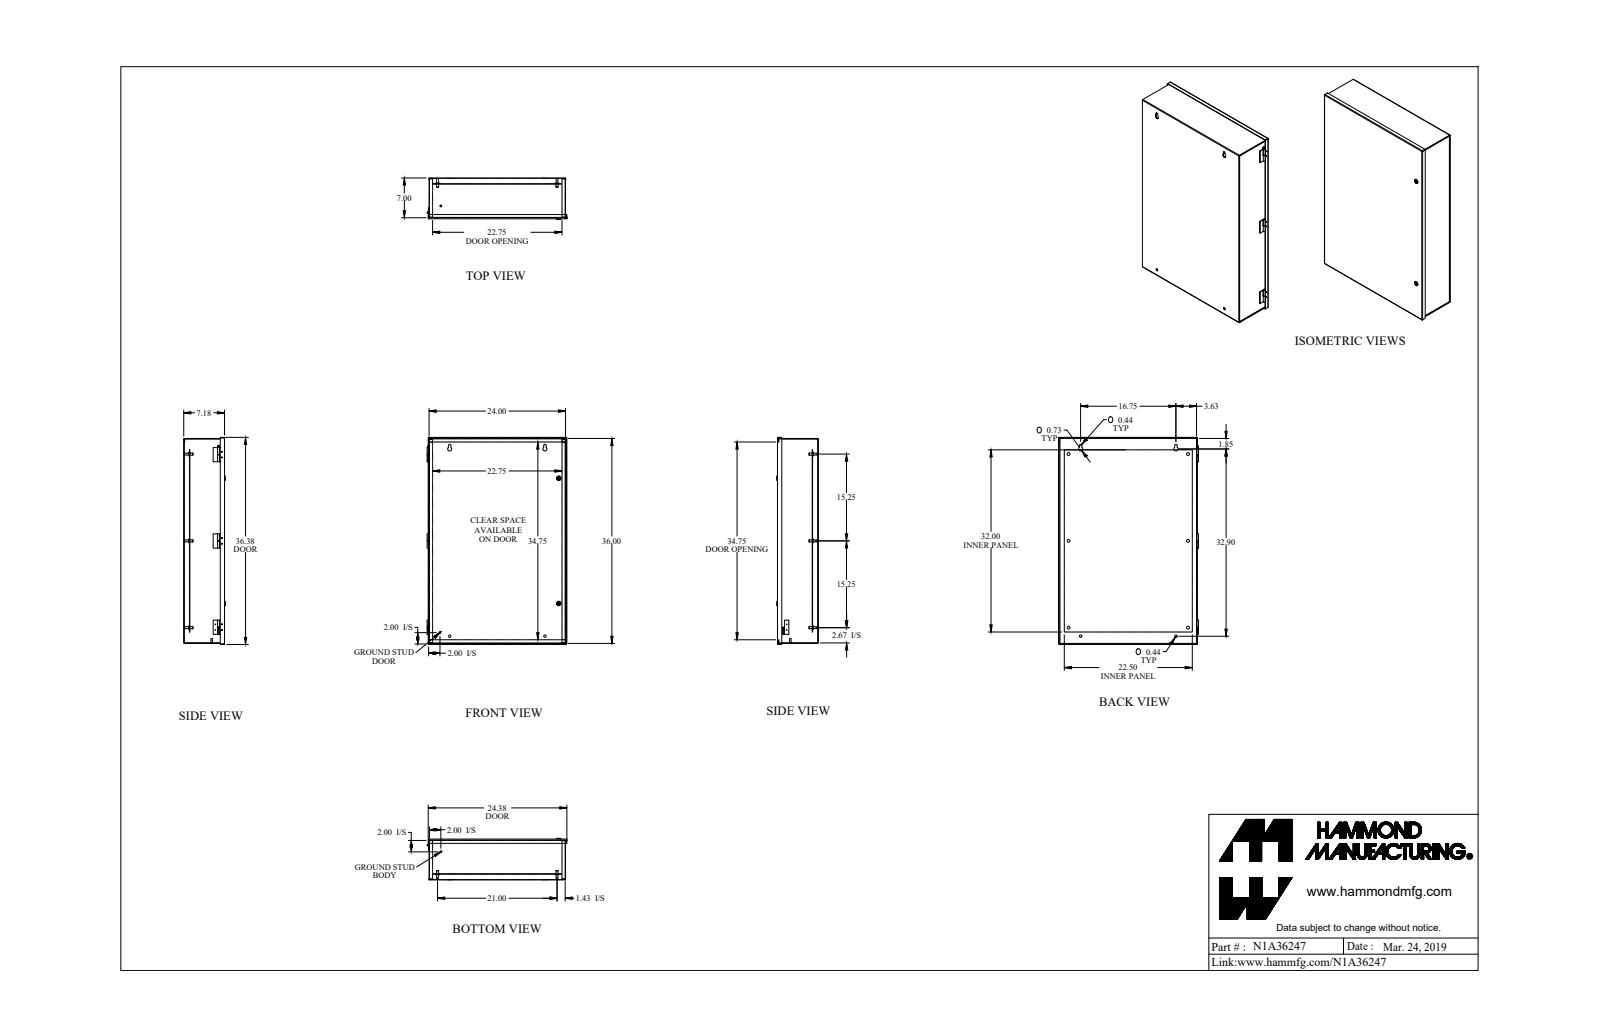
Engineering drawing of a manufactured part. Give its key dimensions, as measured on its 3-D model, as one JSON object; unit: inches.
{"part_name": "N1A36247", "step_written_by": "SolidWorks 2018 (AUTOMOTIVE_DESIGN)", "units": "inches", "bodies": {"solids": 34, "faces": 767, "planar": 434, "cylindrical": 269, "other": 64}, "overall_size": [36.384, 24.574, 7.299], "volume_in3": 255.5, "surface_area_in2": 7114, "round_holes": [[0.14, 12], [0.5, 6], [0.307, 4], [0.445, 4], [0.437, 2], [0.516, 2], [0.734, 2], [0.17, 1], [0.187, 1]], "round_bosses_or_shafts": [[0.128, 12], [0.375, 7], [0.65, 6], [0.33, 6], [1, 4], [0.788, 2], [0.535, 2], [0.496, 2]], "partial_cylinders_radius": [[0.036, 16], [0.108, 16], [0.06, 2], [0.125, 2], [0.153, 2], [0.219, 2], [0.315, 2], [0.03, 1]], "face_to_face_distances": [0.072, 7.105, 1.009, 6.096, 7.033, 7.177, 0.937, 1.081, 6.024, 6.168], "hole_center_spacings": [1, 1.119, 15.157, 15.25, 25.953, 21, 4.26, 11.004]}
